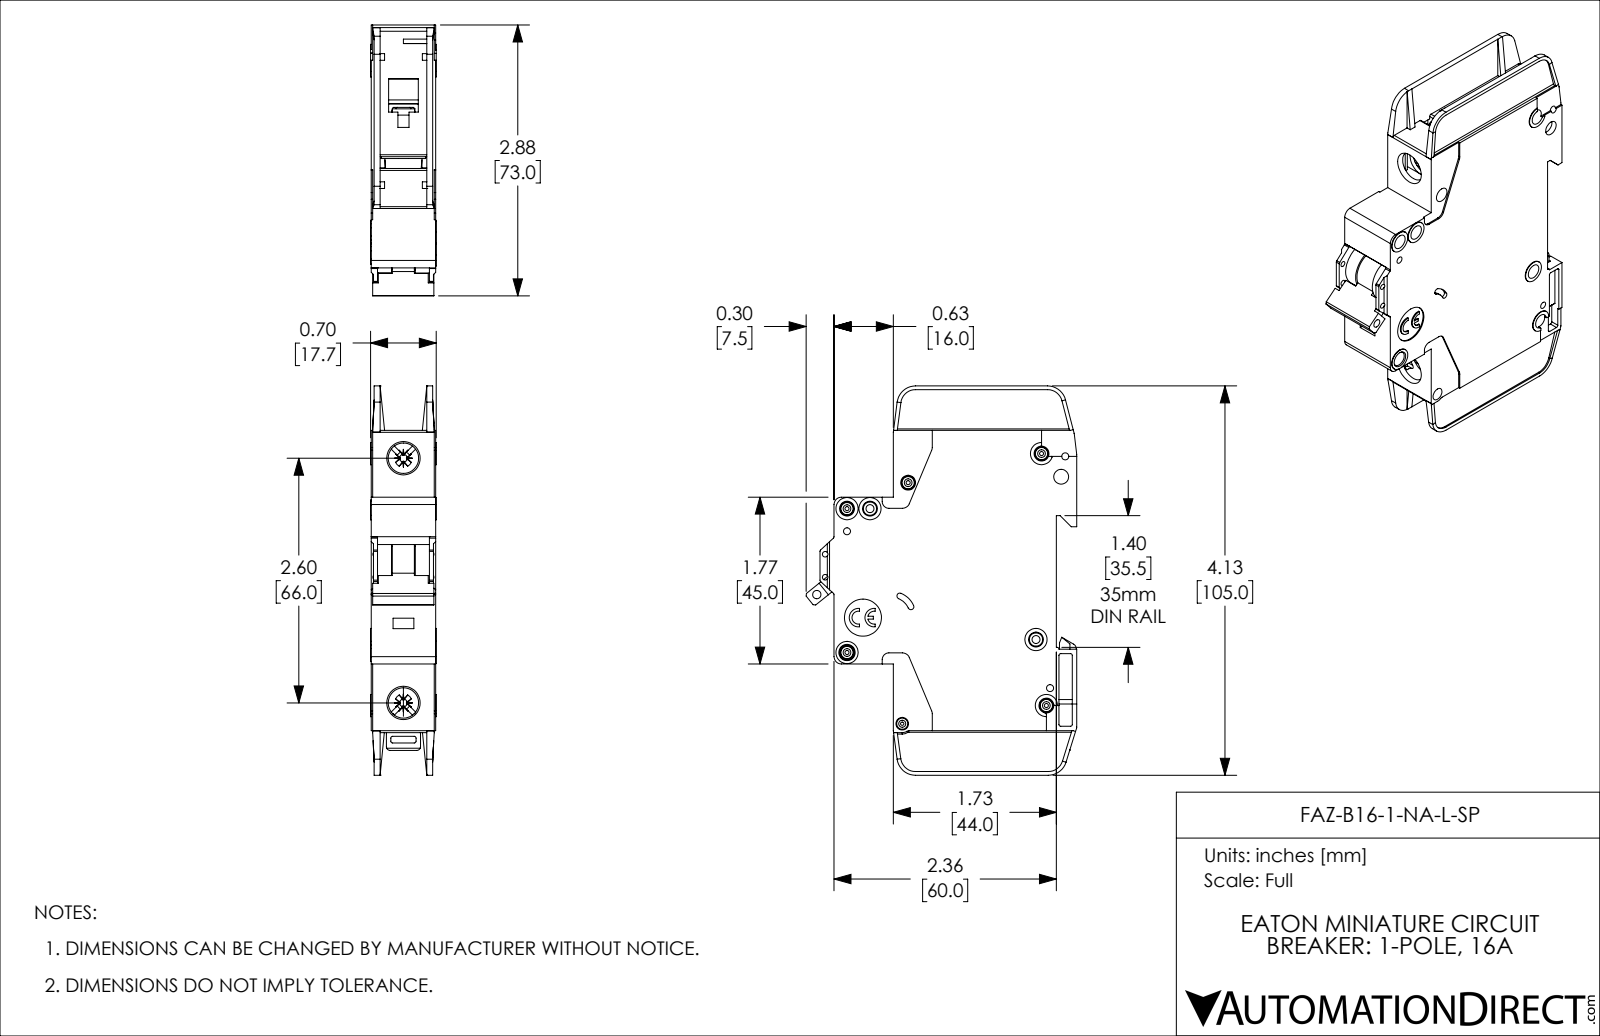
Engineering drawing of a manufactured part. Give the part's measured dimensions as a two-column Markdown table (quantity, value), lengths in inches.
| quantity | value |
| --- | --- |
| part name | FAZ-B16-1-NA-L-SP |
| STEP written by | SolidWorks 2019 (AUTOMOTIVE_DESIGN) |
| units | inches |
| bodies | 1 solid, 1127 faces (671 planar, 357 cylindrical, 99 other) |
| overall size | 4.134 × 2.876 × 0.697 |
| volume | 4.682 in³ |
| surface area | 41.01 in² |
| round holes (diameter × count) | 0.157 × 8, 0.043 × 5, 0.075 × 4, 0.059 × 2, 0.085 × 2, 0.323 × 2, 0.035 × 1, 0.089 × 1, 0.098 × 1, 0.134 × 1, 0.394 × 1 |
| round bosses / shafts (diameter × count) | 0.13 × 5, 0.236 × 4, 0.118 × 2, 0.098 × 1 |
| partial cylindrical surfaces (radius × count) | 0.02 × 42, 0.016 × 10, 0.039 × 10, 0.079 × 8, 0.197 × 5, 0.008 × 4, 0.026 × 4, 0.043 × 4 |
| main face-to-face distances | 0.047, 0.685, 0.591, 0.638, 0.094, 0.543, 0.016, 0.031, 0.496, 0.575 |
| hole center spacings | 0.244, 0.537, 0.87, 0.189, 0.199, 0.204, 0.221, 0.24 |
